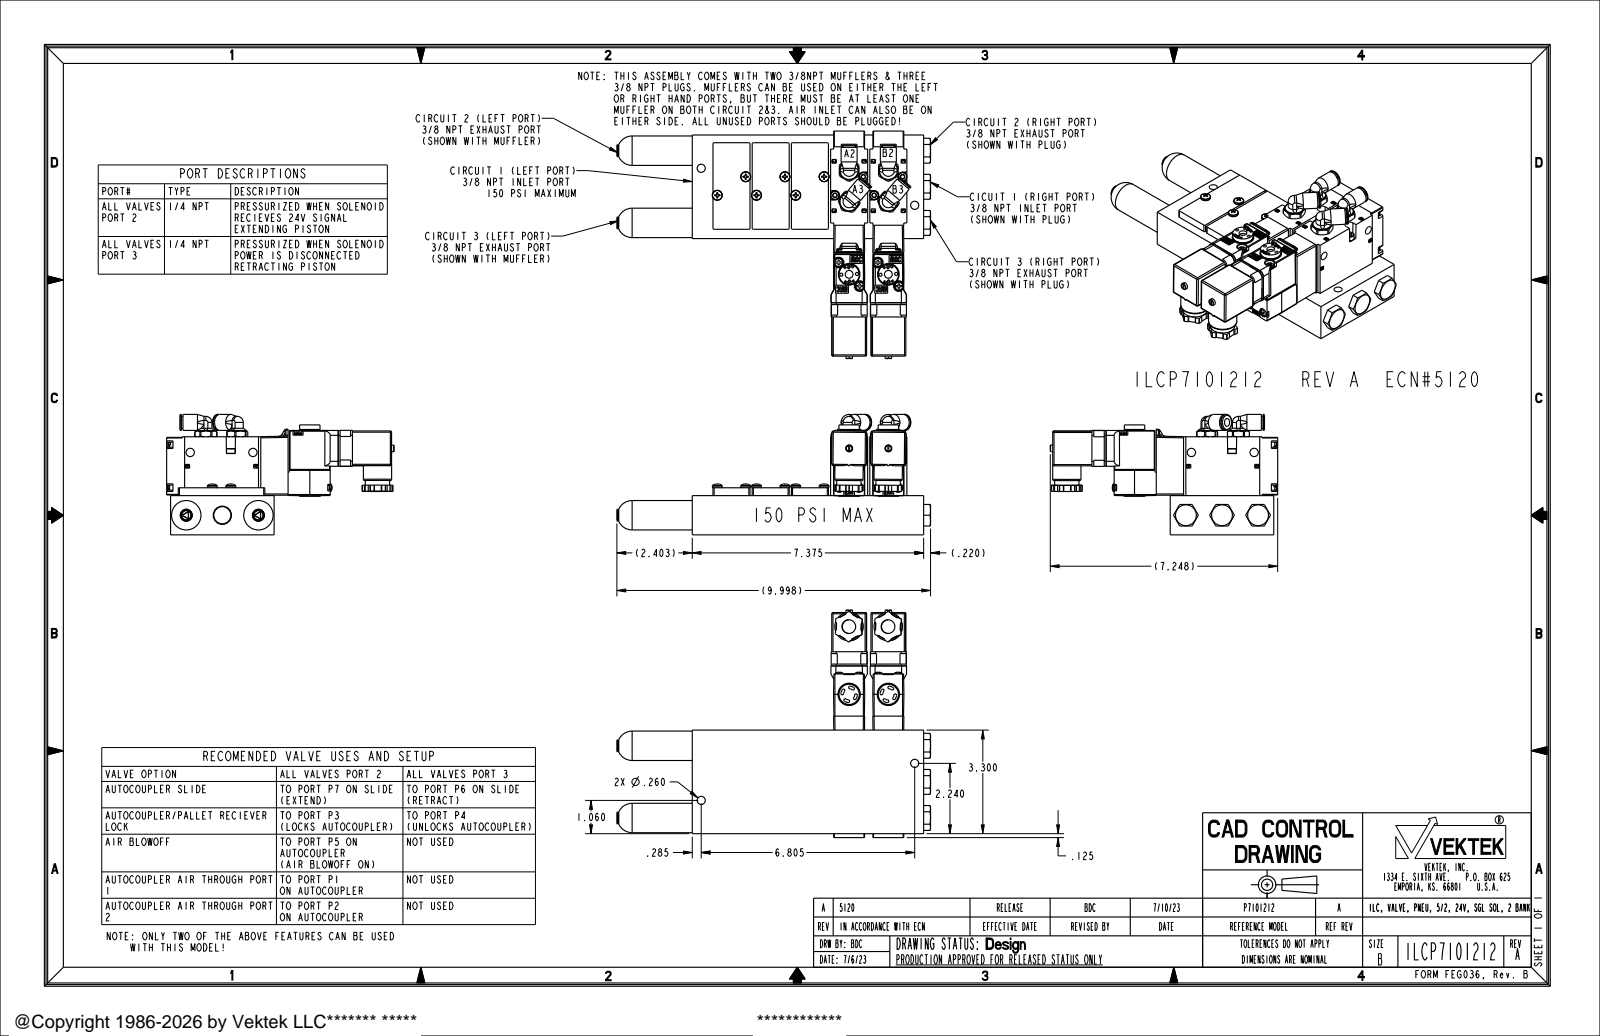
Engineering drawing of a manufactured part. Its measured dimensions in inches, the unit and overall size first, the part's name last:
Units: inches
Overall size (bounding box): 9.998 × 7.248 × 3.837
Round holes (diameter × count): ⌀0.138 ×8, ⌀0.25 ×8, ⌀0.098 ×4, ⌀0.11 ×4, ⌀0.126 ×4, ⌀0.254 ×4, ⌀0.287 ×4, ⌀0.108 ×2, ⌀0.11 ×2, ⌀0.236 ×2, ⌀0.248 ×2, ⌀0.26 ×2
Round bosses / shafts (diameter × count): ⌀0.276 ×12, ⌀0.256 ×8, ⌀0.375 ×6, ⌀0.65 ×4, ⌀0.581 ×4, ⌀0.51 ×4, ⌀0.267 ×4, ⌀0.937 ×2
Partial cylindrical surfaces — rounded edges, fillets, slot ends (radius × count): R0.015 ×72, R0.008 ×48, R0.039 ×40, R0.01 ×28, R0.02 ×25, R0.157 ×24, R0.031 ×23, R0.035 ×16
Main face-to-face distances: 1.25, 1.5, 3.3, 1.25, 0.25, 1.181, 1.083, 0.02, 0.098, 3.126
Hole centre spacings: 1.25, 1.03, 0.508, 0.515, 0.583, 0.589, 1.023, 1.023
Volume: 62.72 in³ · Surface area: 227.7 in²
Bodies: 3 solids, 3024 faces (1584 planar, 726 cylindrical, 714 other)
Part name (STEP PRODUCT): ILCP7101212
STEP written by: CREO PARAMETRIC BY PTC INC, 2021164 (AUTOMOTIVE_DESIGN)
